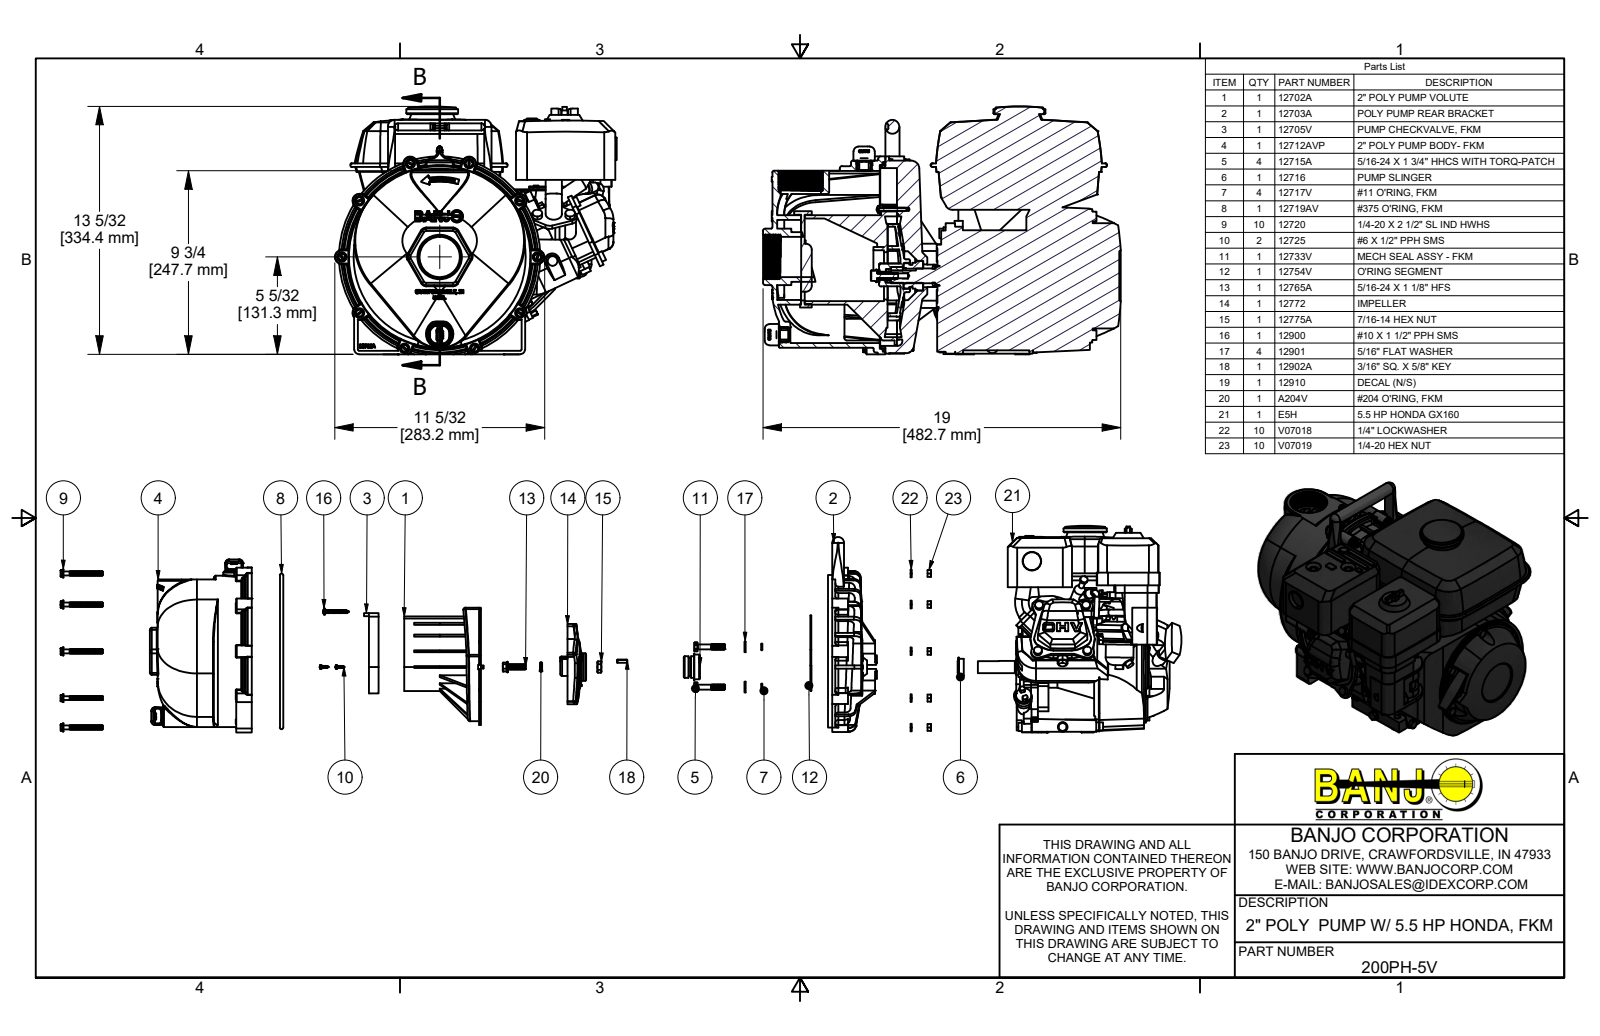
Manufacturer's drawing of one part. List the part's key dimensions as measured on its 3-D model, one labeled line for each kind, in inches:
Part name (STEP PRODUCT): 200PH-5V; 12703A; 12712AVP; X12712A (+8 more)
STEP written by: Autodesk Inventor 2019 (AUTOMOTIVE_DESIGN)
Units: inches
Bodies: 86 solids, 8935 faces (2797 planar, 2274 cylindrical, 3864 other)
Overall size (bounding box): 19.762 × 14.984 × 14.538
Volume: 1 147 in³ · Surface area: 2 846 in²
Round holes (diameter × count): ⌀0.196 ×10, ⌀0.252 ×10, ⌀0.27 ×10, ⌀0.22 ×7, ⌀0.344 ×4, ⌀0.469 ×4, ⌀0.815 ×4, ⌀0.113 ×2, ⌀0.115 ×2, ⌀0.205 ×2, ⌀0.25 ×2, ⌀0.5 ×2
Round bosses / shafts (diameter × count): ⌀0.276 ×80, ⌀0.52 ×10, ⌀0.489 ×10, ⌀0.25 ×10, ⌀0.512 ×6, ⌀0.192 ×6, ⌀0.688 ×4, ⌀0.313 ×4
Partial cylindrical surfaces — rounded edges, fillets, slot ends (radius × count): R0.03 ×116, R0.25 ×33, R0.008 ×26, R0.079 ×24, R0.187 ×24, R0.06 ×23, R0.125 ×23, R0.015 ×13
Main face-to-face distances: 0.18, 0.2, 0.037, 0.163, 2.88, 1.589, 0.11, 0.25, 0.5, 1
Hole centre spacings: 5.2, 1.81, 2.56, 3.128, 6.15, 8.387, 10.4, 1.31
